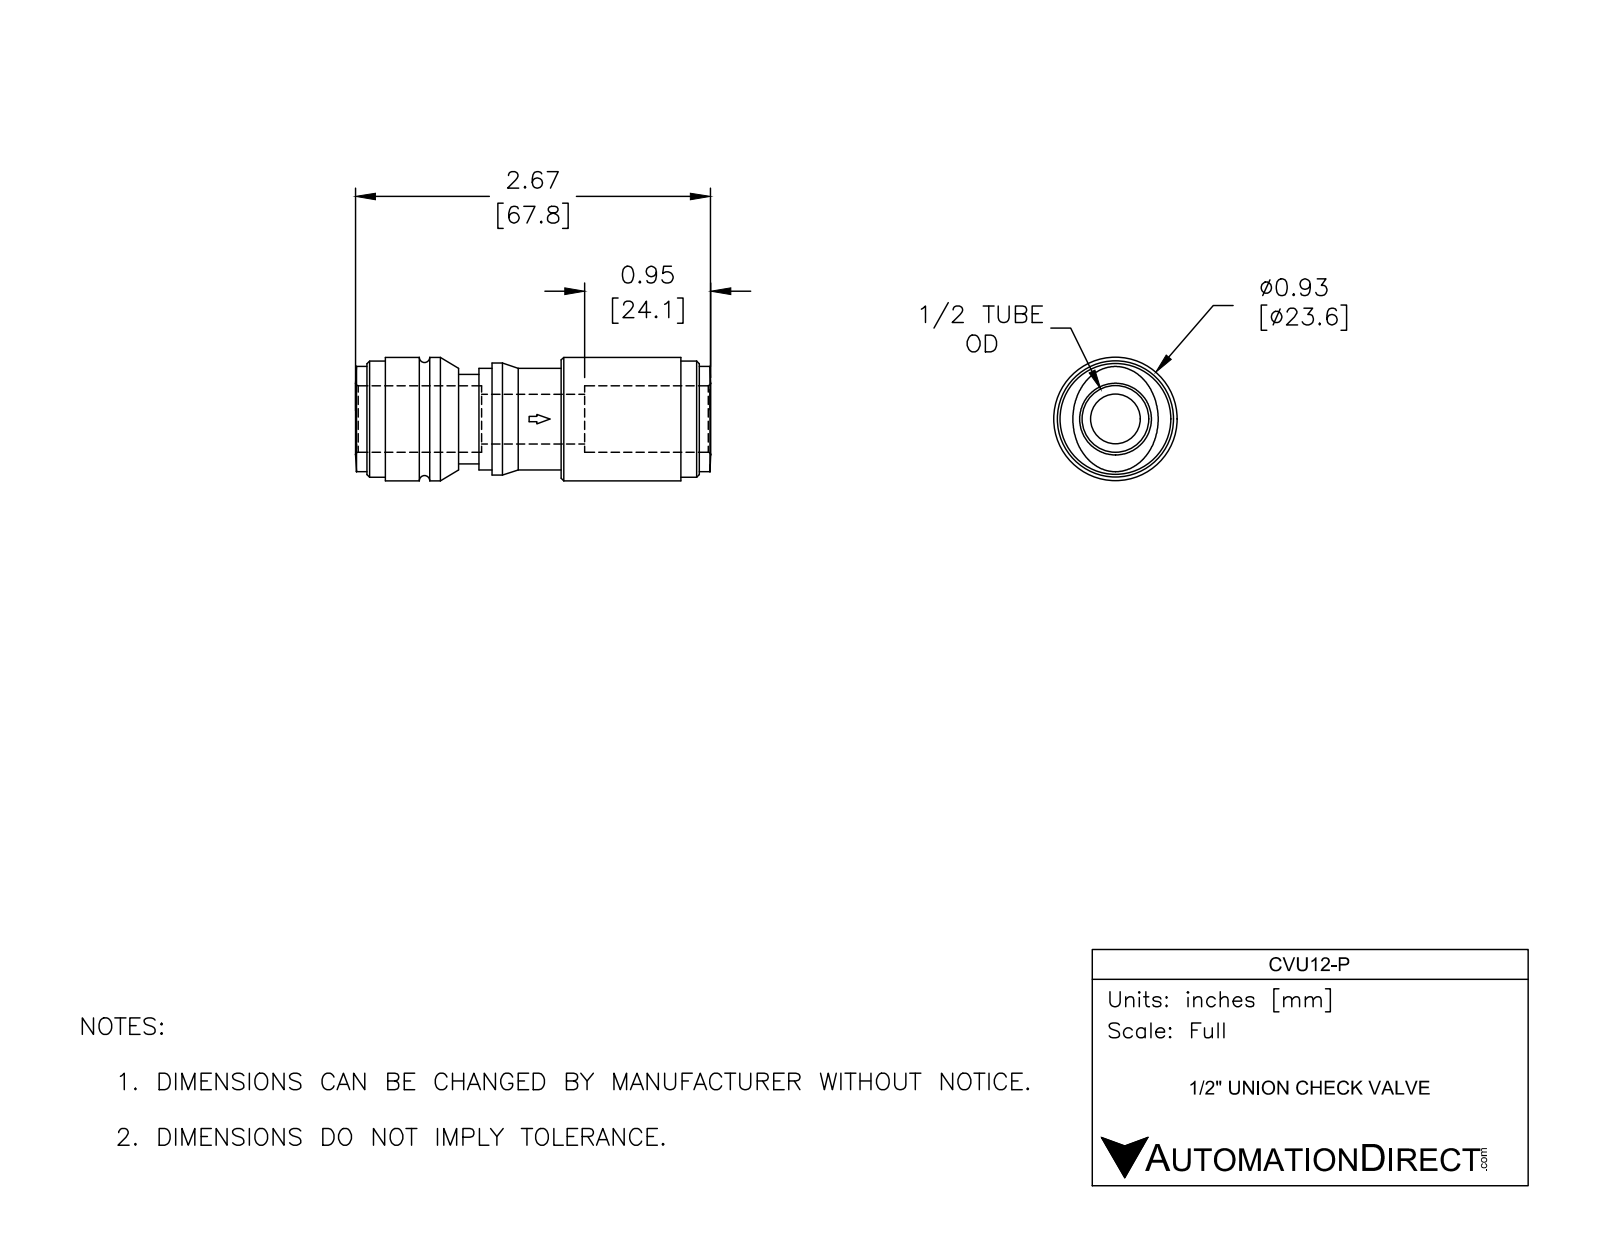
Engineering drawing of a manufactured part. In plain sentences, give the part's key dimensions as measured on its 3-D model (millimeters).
The part is named "CVU12-P". Its 3-D file was written by "SolidWorks 2017 (AUTOMOTIVE_DESIGN)". It is 1 solid with 68 faces: 17 planar, 25 cylindrical and 26 other. Overall it measures 67.9 by 23.6 by 23.6 millimeters. Its volume is 17 810 cubic millimeters and its surface area 8 245 square millimeters. Round holes: 1 of diameter 9.5, 1 of diameter 12.7. Round bosses or shafts: 1 of diameter 23.6, 1 of diameter 22.2, 1 of diameter 21.4, 1 of diameter 19.4, 1 of diameter 17.1. Partial cylindrical surfaces (rounded edges, fillets, slot ends): 1 of radius 9.8. The main face-to-face distances are 21.9, 41.6, 3.5, 60, 18.4, 38.1, 26.4, 63.5, 37.1, 46.
